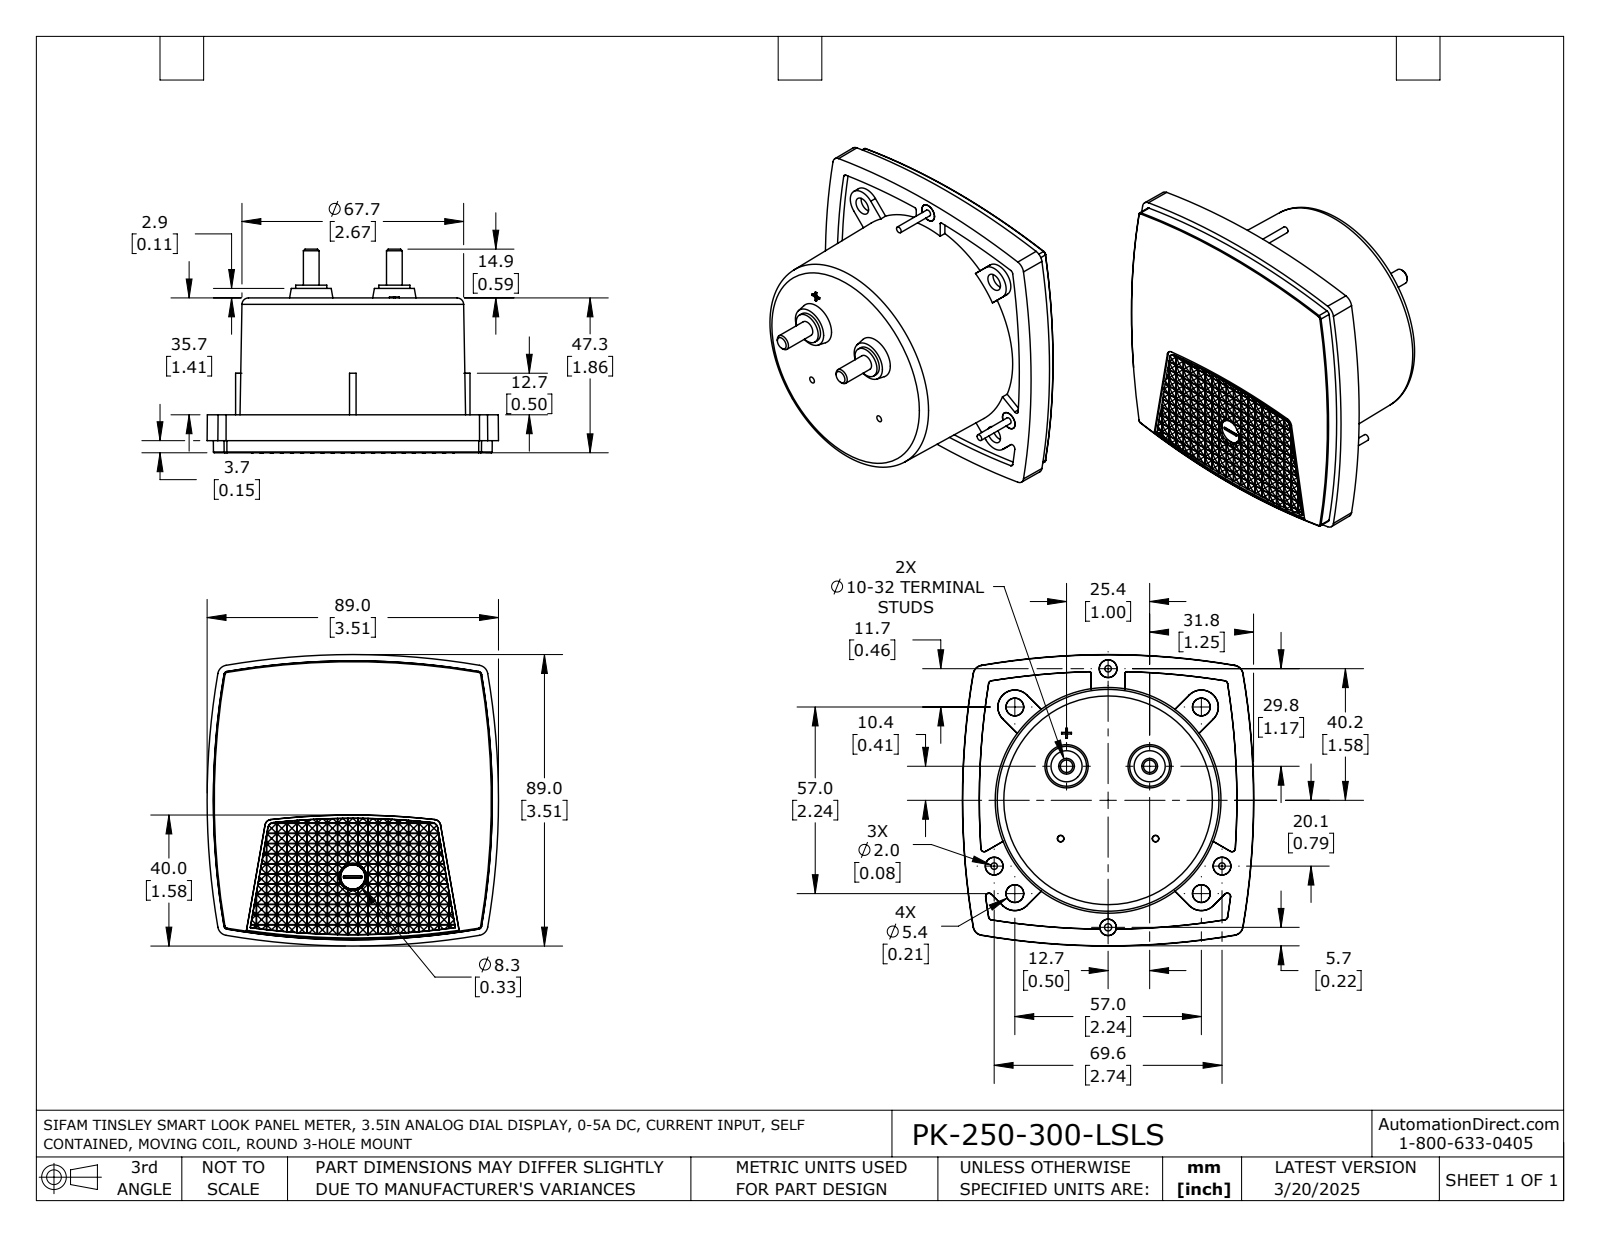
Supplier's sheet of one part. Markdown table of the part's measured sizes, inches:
| quantity | value |
| --- | --- |
| part name | PK-250-300-LSLS |
| STEP written by | SolidWorks 2021 (AUTOMOTIVE_DESIGN) |
| units | inches |
| bodies | 1 solid, 1078 faces (950 planar, 23 cylindrical, 105 other) |
| overall size | 3.505 × 3.505 × 2.453 |
| volume | 12.99 in³ |
| surface area | 44.29 in² |
| round holes (diameter × count) | 0.087 × 1 |
| round bosses / shafts (diameter × count) | 0.213 × 3, 0.079 × 3, 0.374 × 2, 0.189 × 2 |
| partial cylindrical surfaces (radius × count) | 8.961 × 1 |
| main face-to-face distances | 1.862, 1.406, 0.457, 0.079, 1.484, 0.378, 0.024, 0.096, 0.072, 0.12 |
